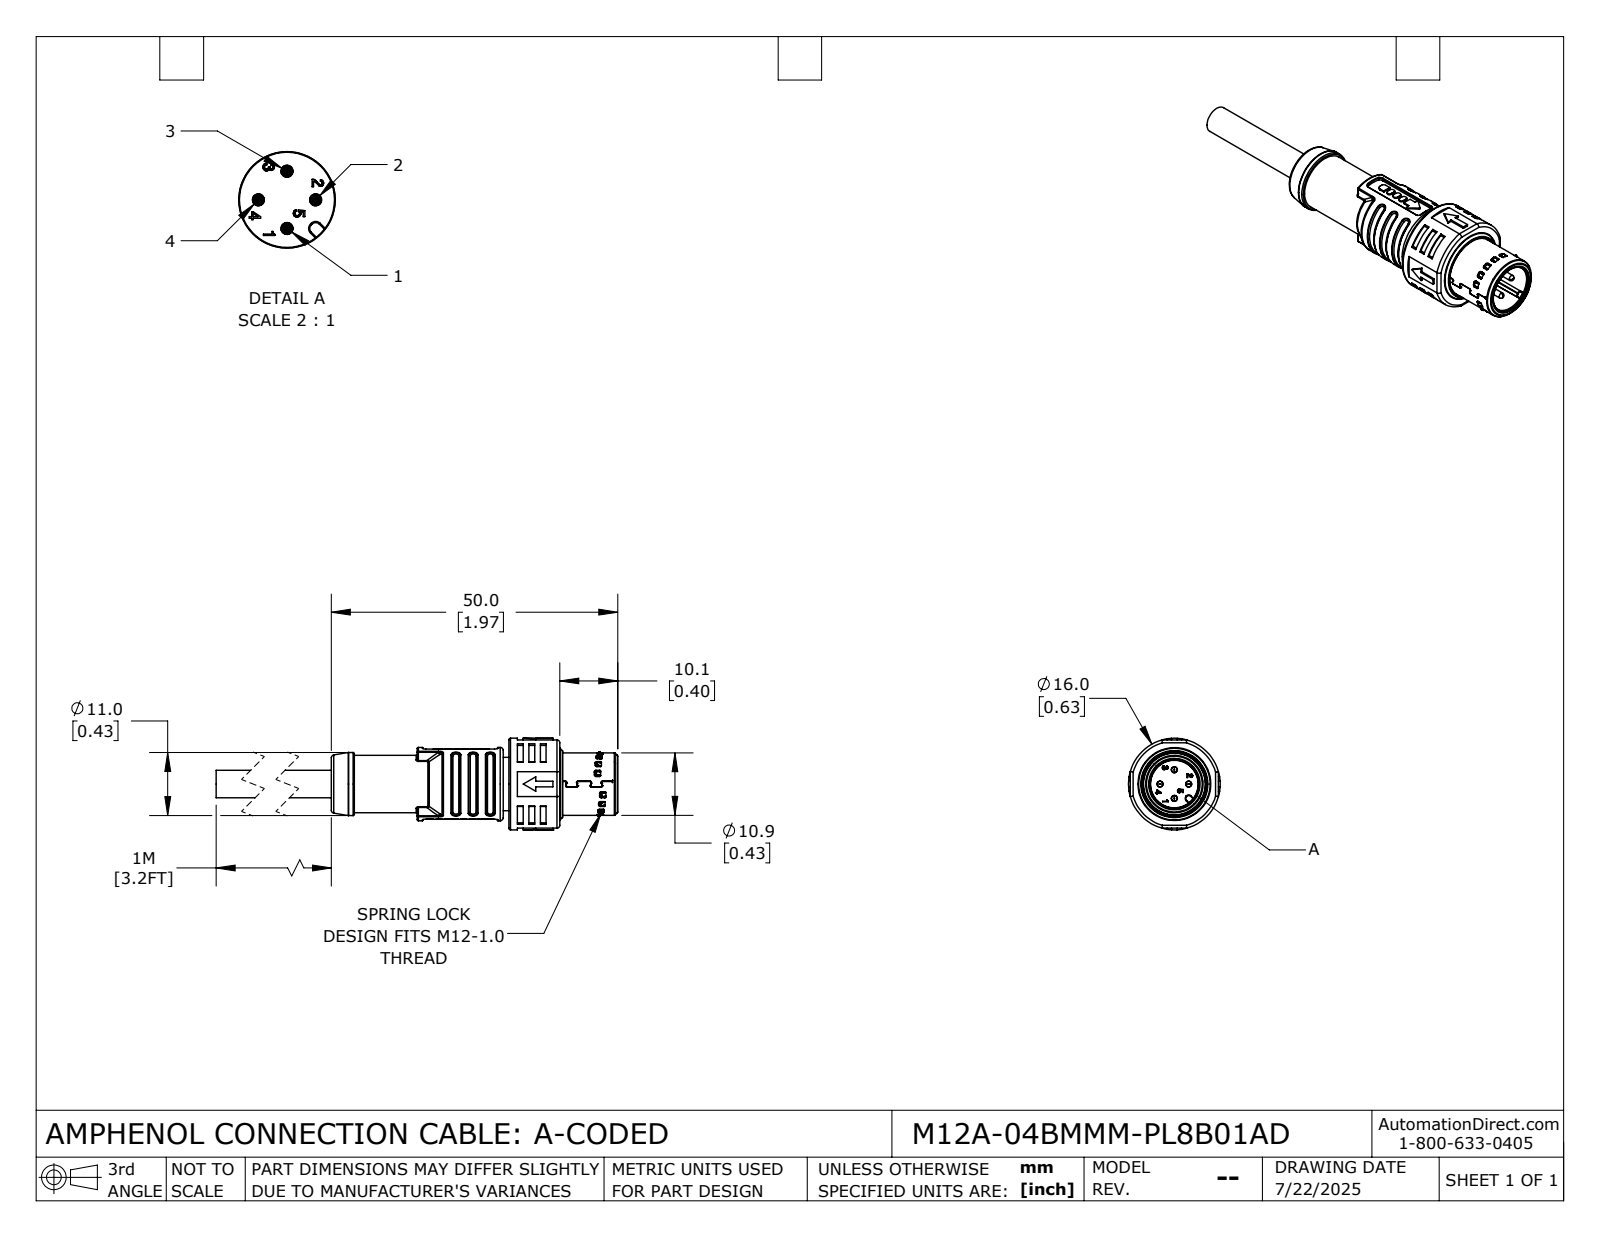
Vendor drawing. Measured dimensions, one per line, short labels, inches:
name: M12A-04BMMM-PL8B01AD
written by: SolidWorks 2024 (CONFIG_CONTROL_DESIGN)
unit: in
bodies: 1 solid, 2276 faces (1081 planar, 672 cylindrical, 523 other)
size: 2.862 × 0.63 × 0.63
volume: 0.316 in³; area: 9.253 in²
holes: 4× ⌀0.041, 4× ⌀0.057, 1× ⌀0.327, 1× ⌀0.354, 1× ⌀0.4, 1× ⌀0.413, 1× ⌀0.453, 1× ⌀0.465, 1× ⌀0.559
bosses: 4× ⌀0.055, 4× ⌀0.039, 1× ⌀0.63, 1× ⌀0.555, 1× ⌀0.504, 1× ⌀0.488, 1× ⌀0.433, 1× ⌀0.429
rounds: 114× R0.008, 66× R0.01, 64× R0.012, 44× R0.006, 38× R0.02, 12× R0.005, 11× R0.028, 10× R0.004
face distances: 0.039, 0.398, 0.35, 0.339, 0.098, 0.059, 0.047, 1.28, 0.606, 1.618
hole spacings: 0.098, 0.139, 0.197
